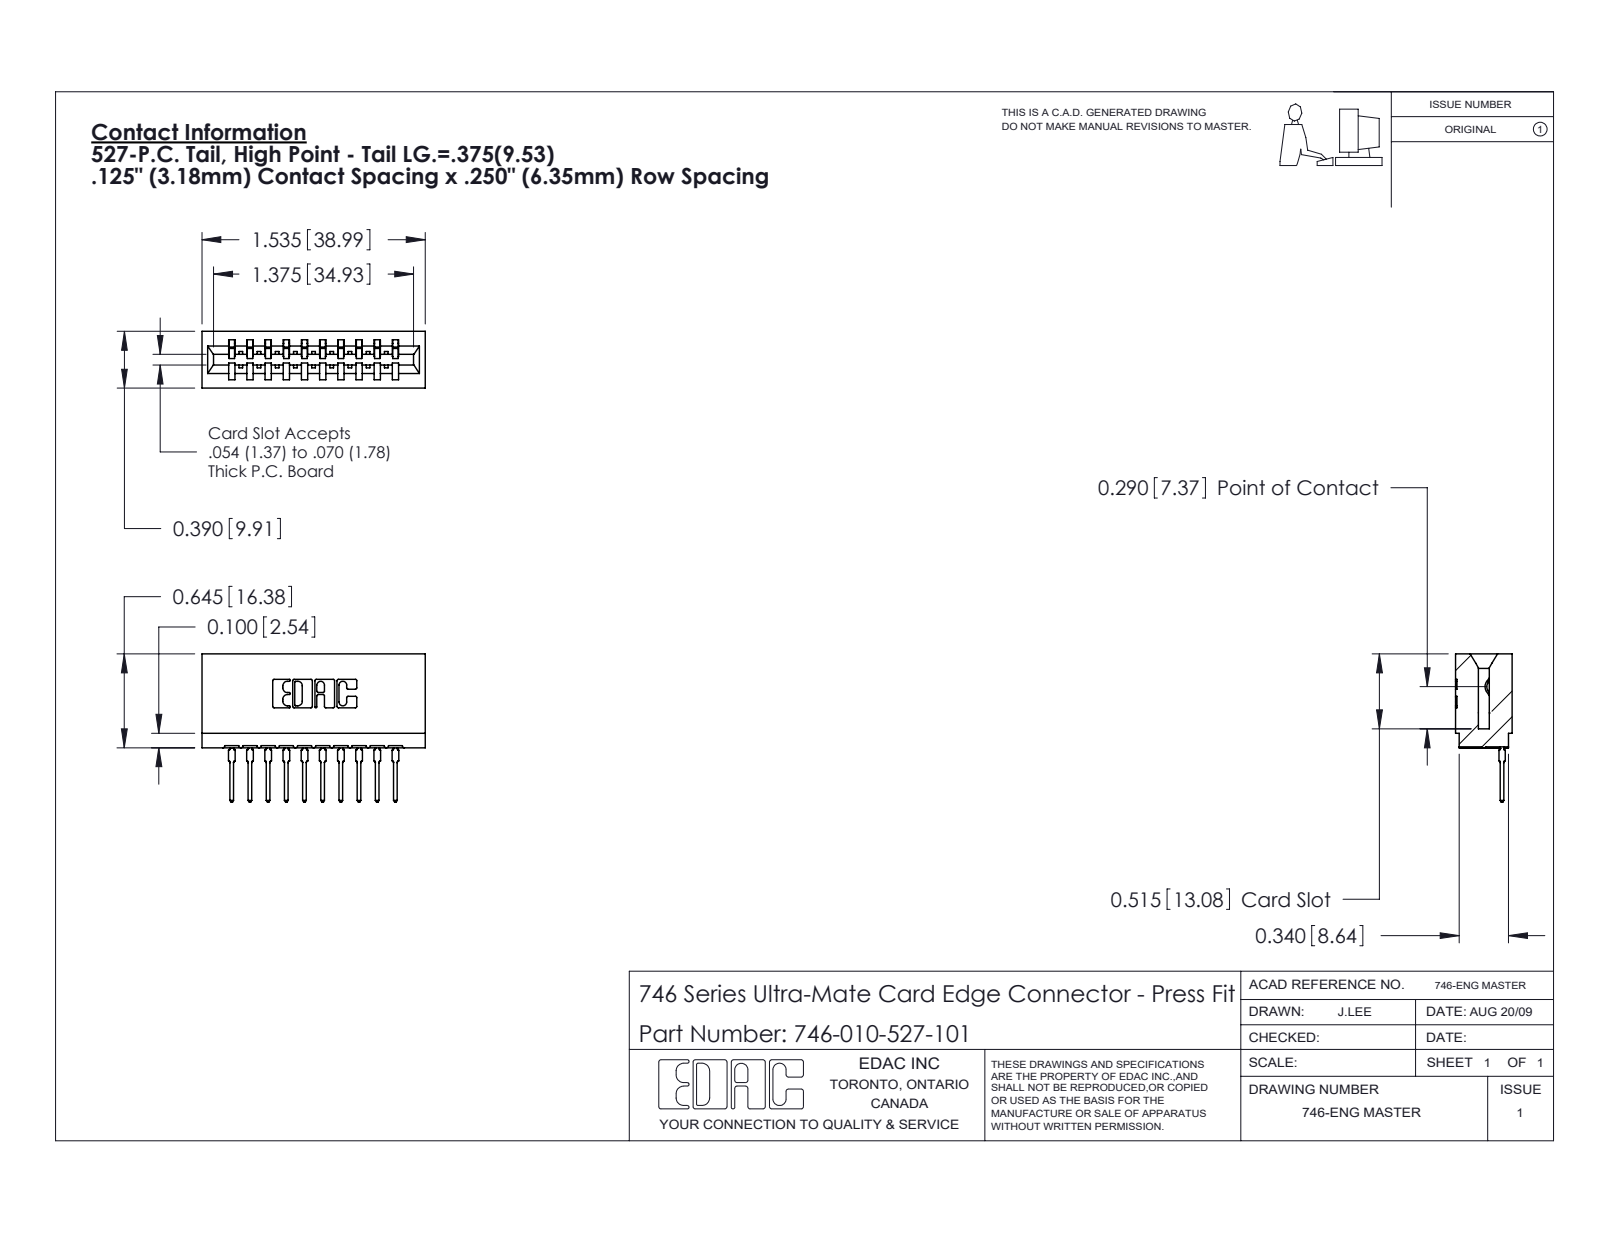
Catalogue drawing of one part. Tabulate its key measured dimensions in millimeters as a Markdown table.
| quantity | value |
| --- | --- |
| part name | 746-292-001_527; 746-010-527-101; 746 Part_.515 Slot Depth - 01 |
| STEP written by | SolidWorks 2020 (CONFIG_CONTROL_DESIGN) |
| units | millimeters |
| bodies | 11 solids, 1177 faces (685 planar, 232 cylindrical, 260 other) |
| overall size | 39 × 25.9 × 9.9 |
| volume | 4 310 mm³ |
| surface area | 5 895 mm² |
| partial cylindrical surfaces (radius × count) | 0.3 × 22, 0.5 × 20, 0.4 × 11, 0.2 × 6, 0.8 × 6, 0.1 × 4, 0.3 × 4, 0.7 × 3 |
| main face-to-face distances | 6.4, 12.7, 8.5, 3.2, 1.1, 1.4, 9.5, 5.3, 3.2, 9.9 |
